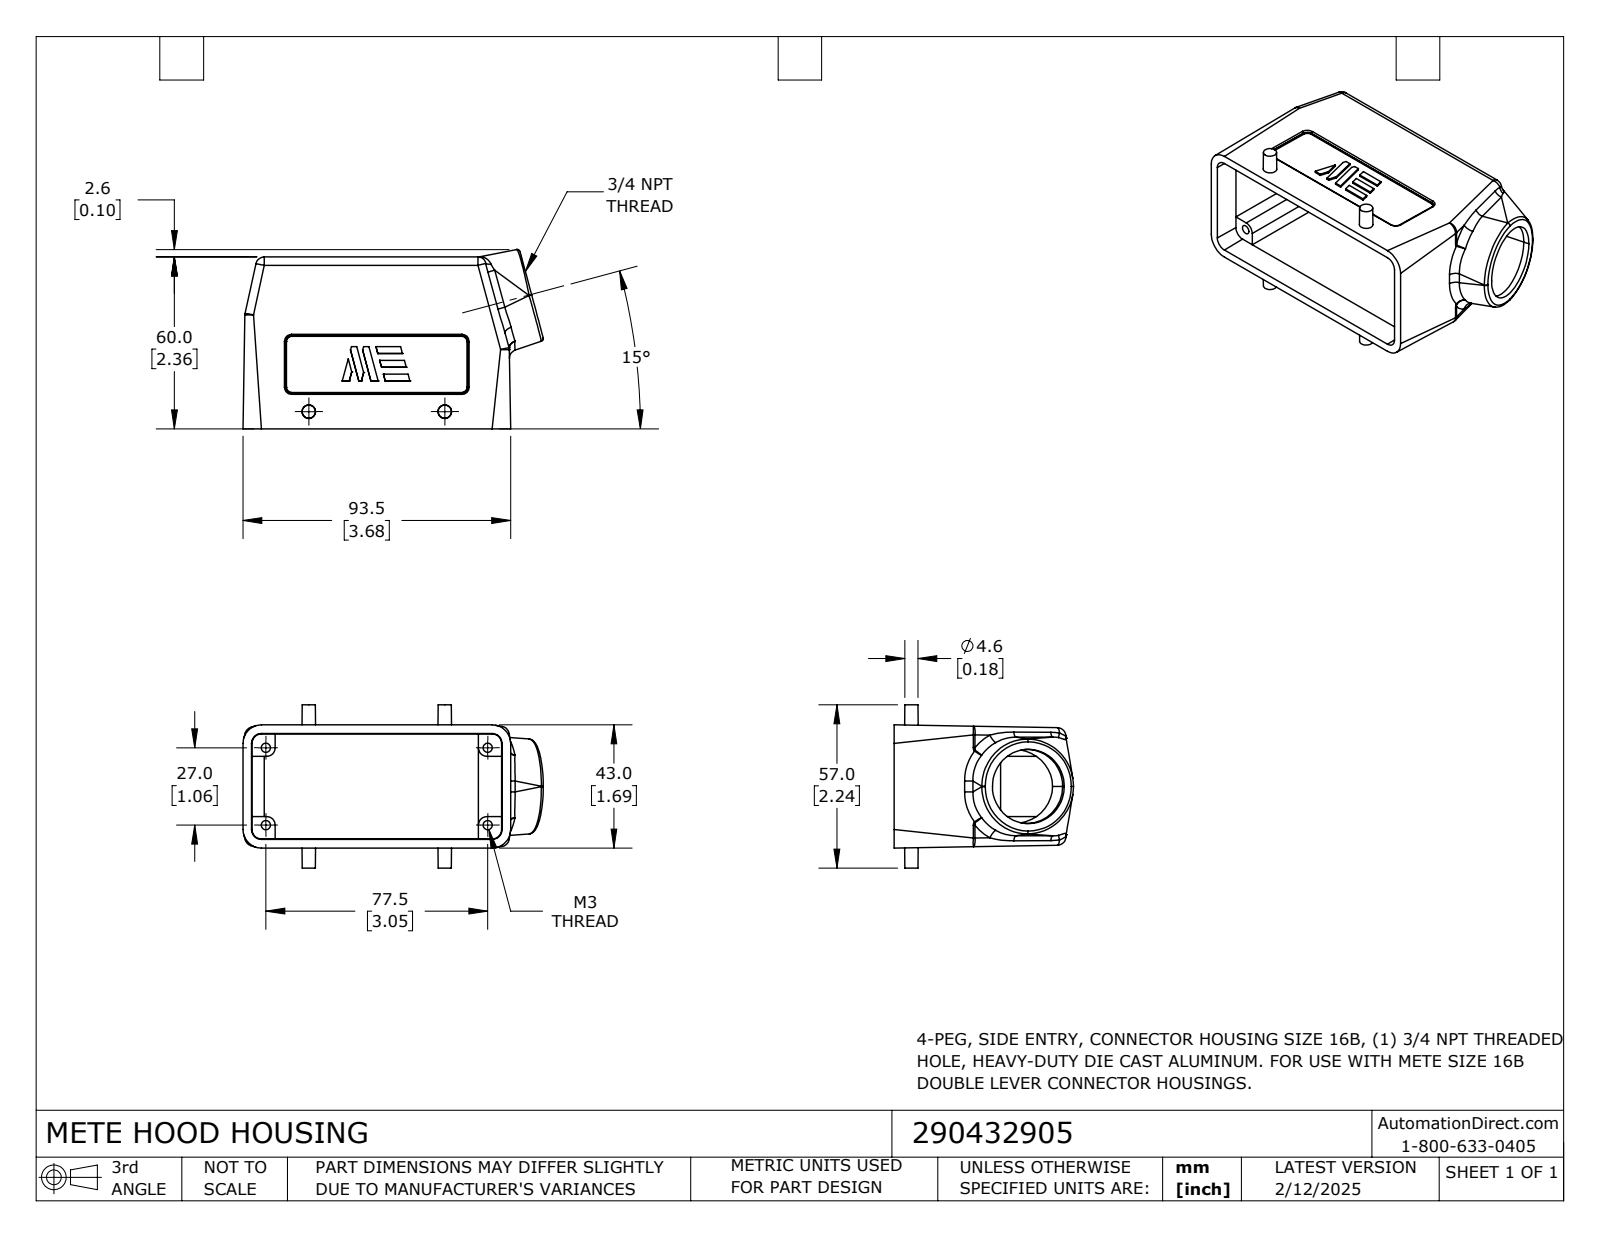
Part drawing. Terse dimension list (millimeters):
name: 290432905
written by: SolidWorks 2024 (CONFIG_CONTROL_DESIGN)
unit: mm
bodies: 1 solid, 251 faces (120 planar, 53 cylindrical, 78 other)
size: 104.9 × 62.6 × 57
volume: 60 880 mm³; area: 38 520 mm²
holes: 4× ⌀3.2
rounds: 14× R3, 8× R0.2, 8× R0.5, 8× R2, 2× R2.5, 1× R1
face distances: 3, 36.7, 0.8, 2.2, 79.1, 57, 8.1, 60, 7.8, 28.8
hole spacings: 27, 77.5, 82.1
